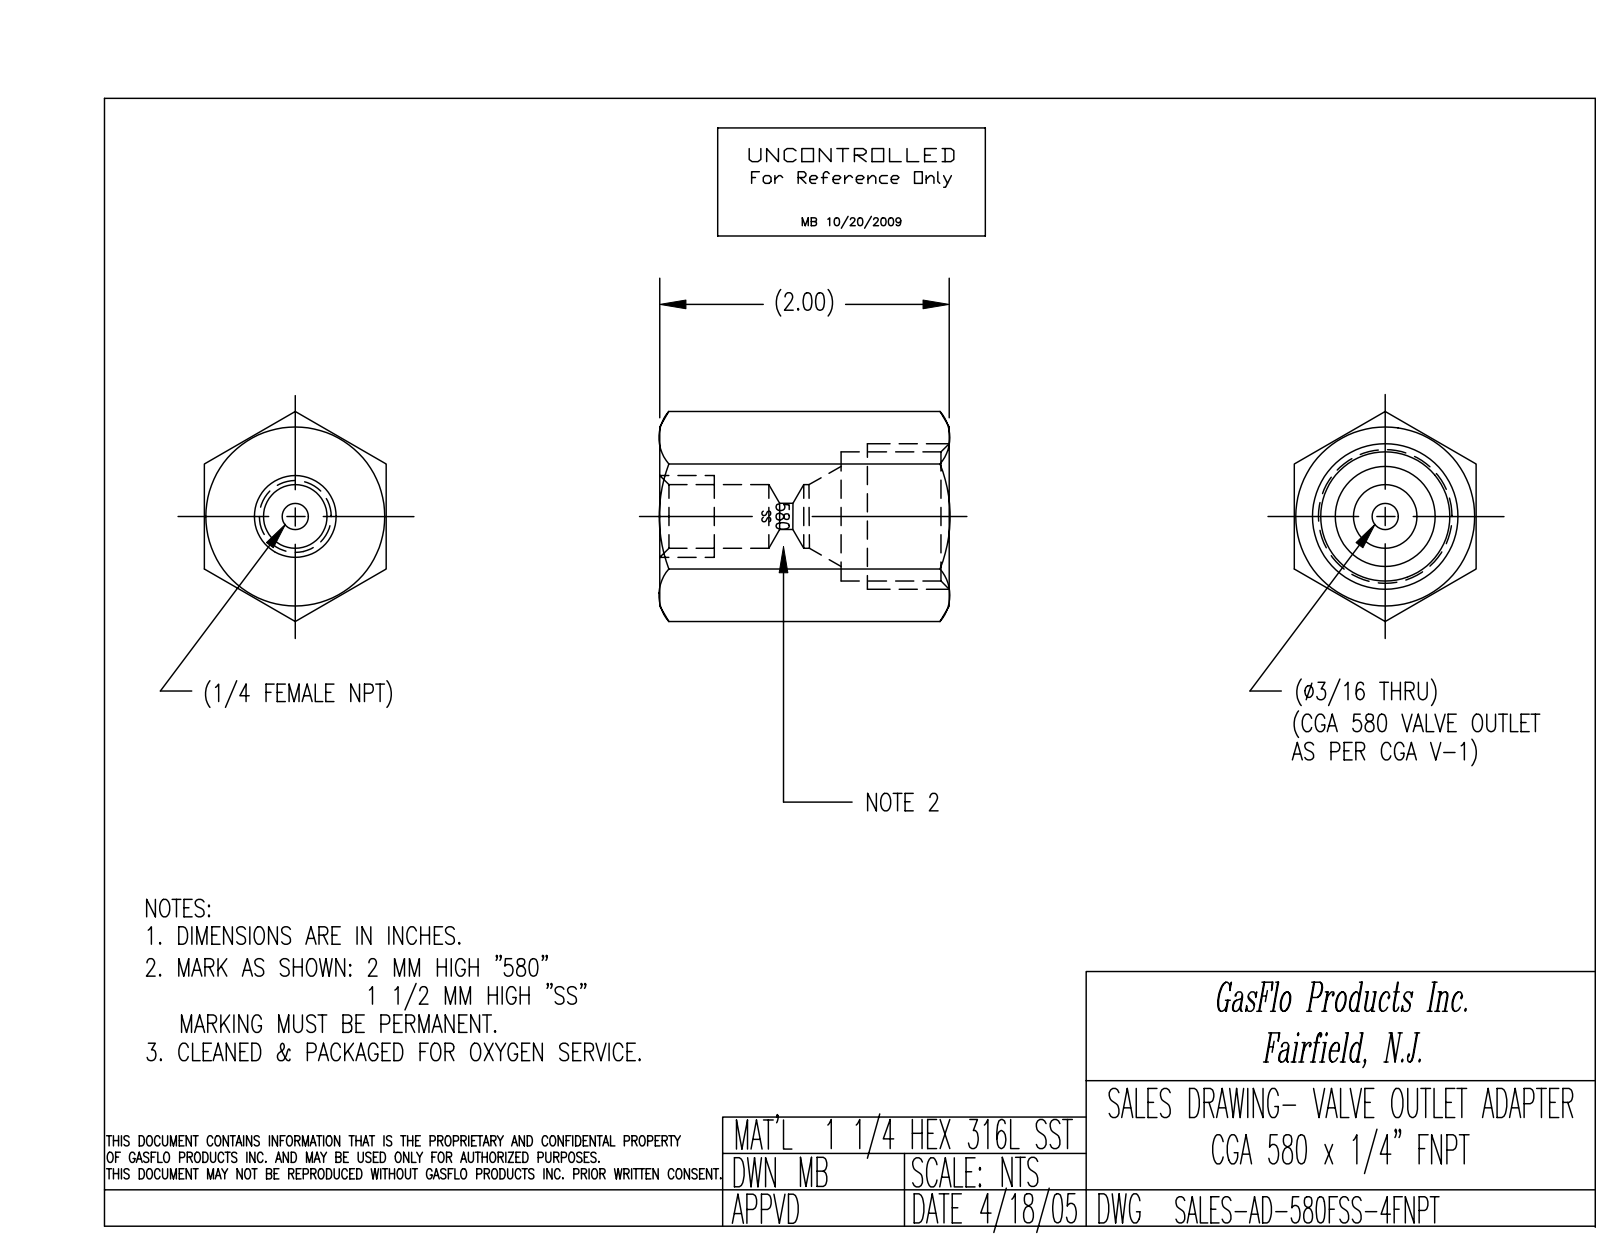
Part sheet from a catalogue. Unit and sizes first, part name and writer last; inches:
Units: inches
Overall size (bounding box): 2 × 1.443 × 1.25
Round holes (diameter × count): ⌀0.187 ×1, ⌀0.422 ×1, ⌀0.422 ×1, ⌀0.892 ×1
Main face-to-face distances: 1.25, 1.25, 2, 1.313, 0.687
Volume: 2.033 in³ · Surface area: 16.16 in²
Bodies: 1 solid, 76 faces (17 planar, 25 cylindrical, 34 other)
Part name (STEP PRODUCT): AD-580FSS-4FNPT
STEP written by: SolidWorks 2018 (CONFIG_CONTROL_DESIGN)
